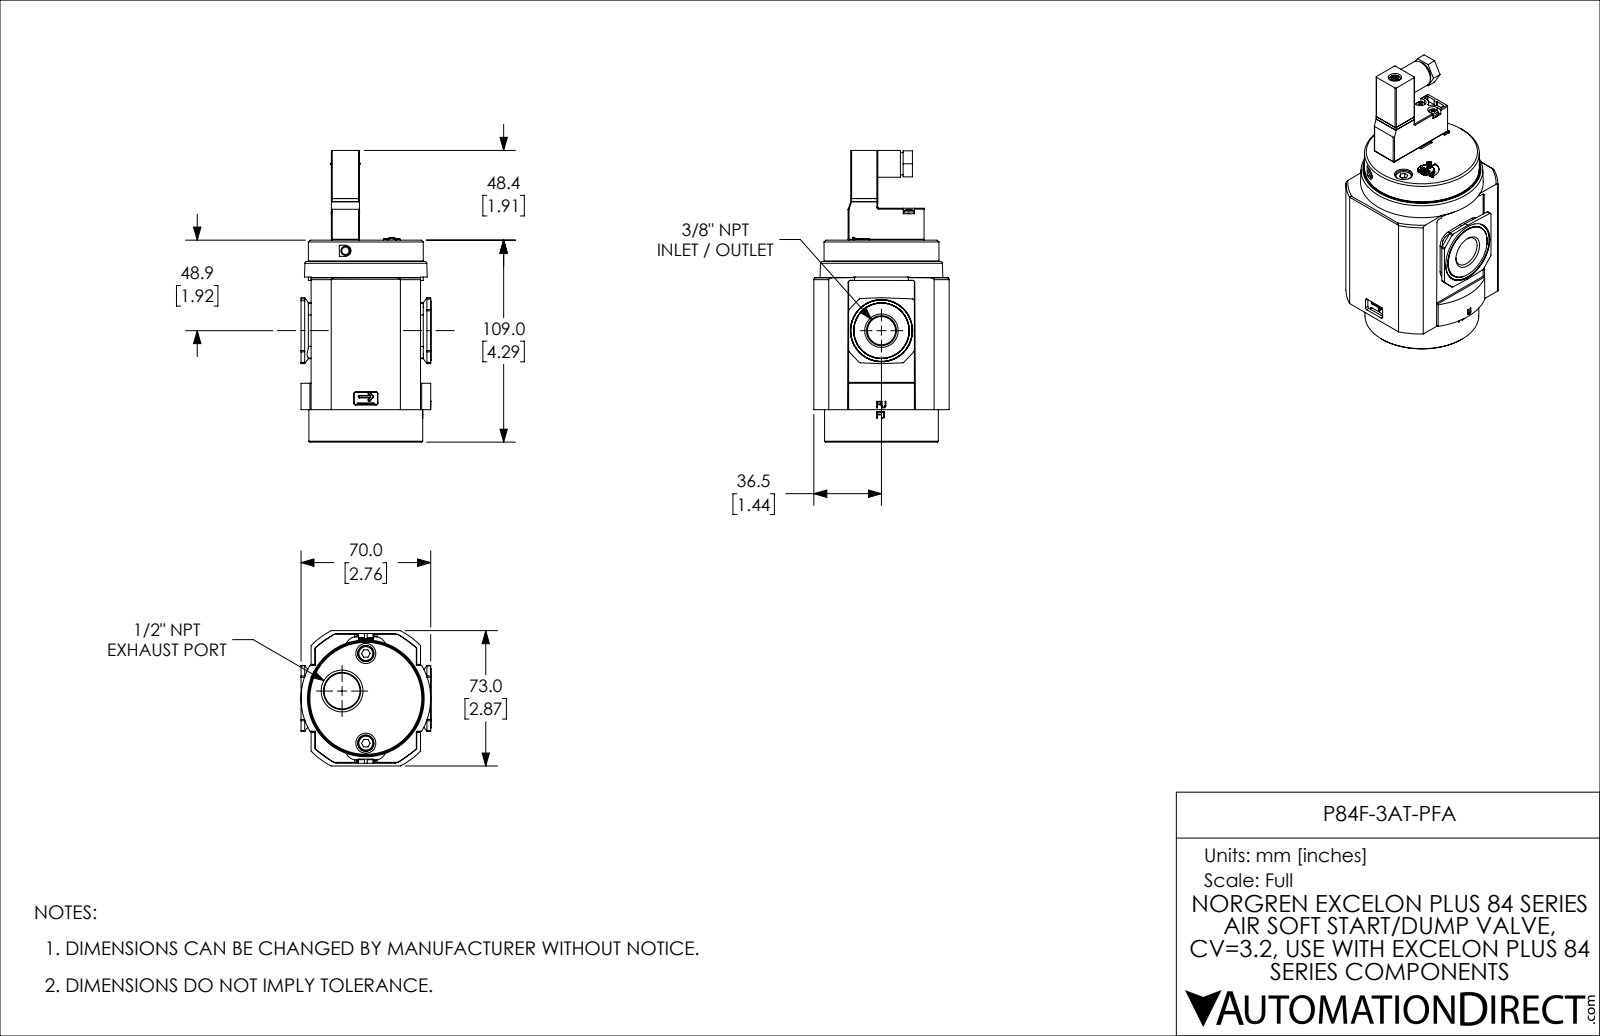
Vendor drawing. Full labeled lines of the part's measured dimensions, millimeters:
Part name (STEP PRODUCT): P84F-3AT-PFA
STEP written by: SolidWorks 2021 (CONFIG_CONTROL_DESIGN)
Units: millimetres
Bodies: 8 solids, 1169 faces (576 planar, 354 cylindrical, 239 other)
Overall size (bounding box): 157.35 × 73 × 70.25
Volume: 419 656 mm³ · Surface area: 97 088 mm²
Round holes (diameter × count): ⌀4.92 ×4, ⌀5.3 ×4, ⌀8.8 ×4, ⌀1.5 ×3, ⌀2.46 ×3, ⌀0.8 ×2, ⌀1.9 ×2, ⌀3.1 ×2, ⌀8.5 ×2, ⌀1.78 ×1, ⌀3 ×1, ⌀3.8 ×1
Round bosses / shafts (diameter × count): ⌀8.5 ×4, ⌀5 ×4, ⌀3 ×2, ⌀62 ×1, ⌀61.4 ×1, ⌀59 ×1, ⌀14.5 ×1, ⌀12 ×1
Partial cylindrical surfaces — rounded edges, fillets, slot ends (radius × count): R0.5 ×34, R0.25 ×14, R1 ×13, R3 ×4, R6 ×4, R6.3 ×4, R0.26 ×3, R0.34 ×3
Main face-to-face distances: 1.5, 70.2, 2, 71, 71.5, 0.5, 69.5, 70, 11.25, 81.45
Hole centre spacings: 3.8, 5.05, 5.41, 7.11, 12.41, 21.05, 24.88, 46.75
